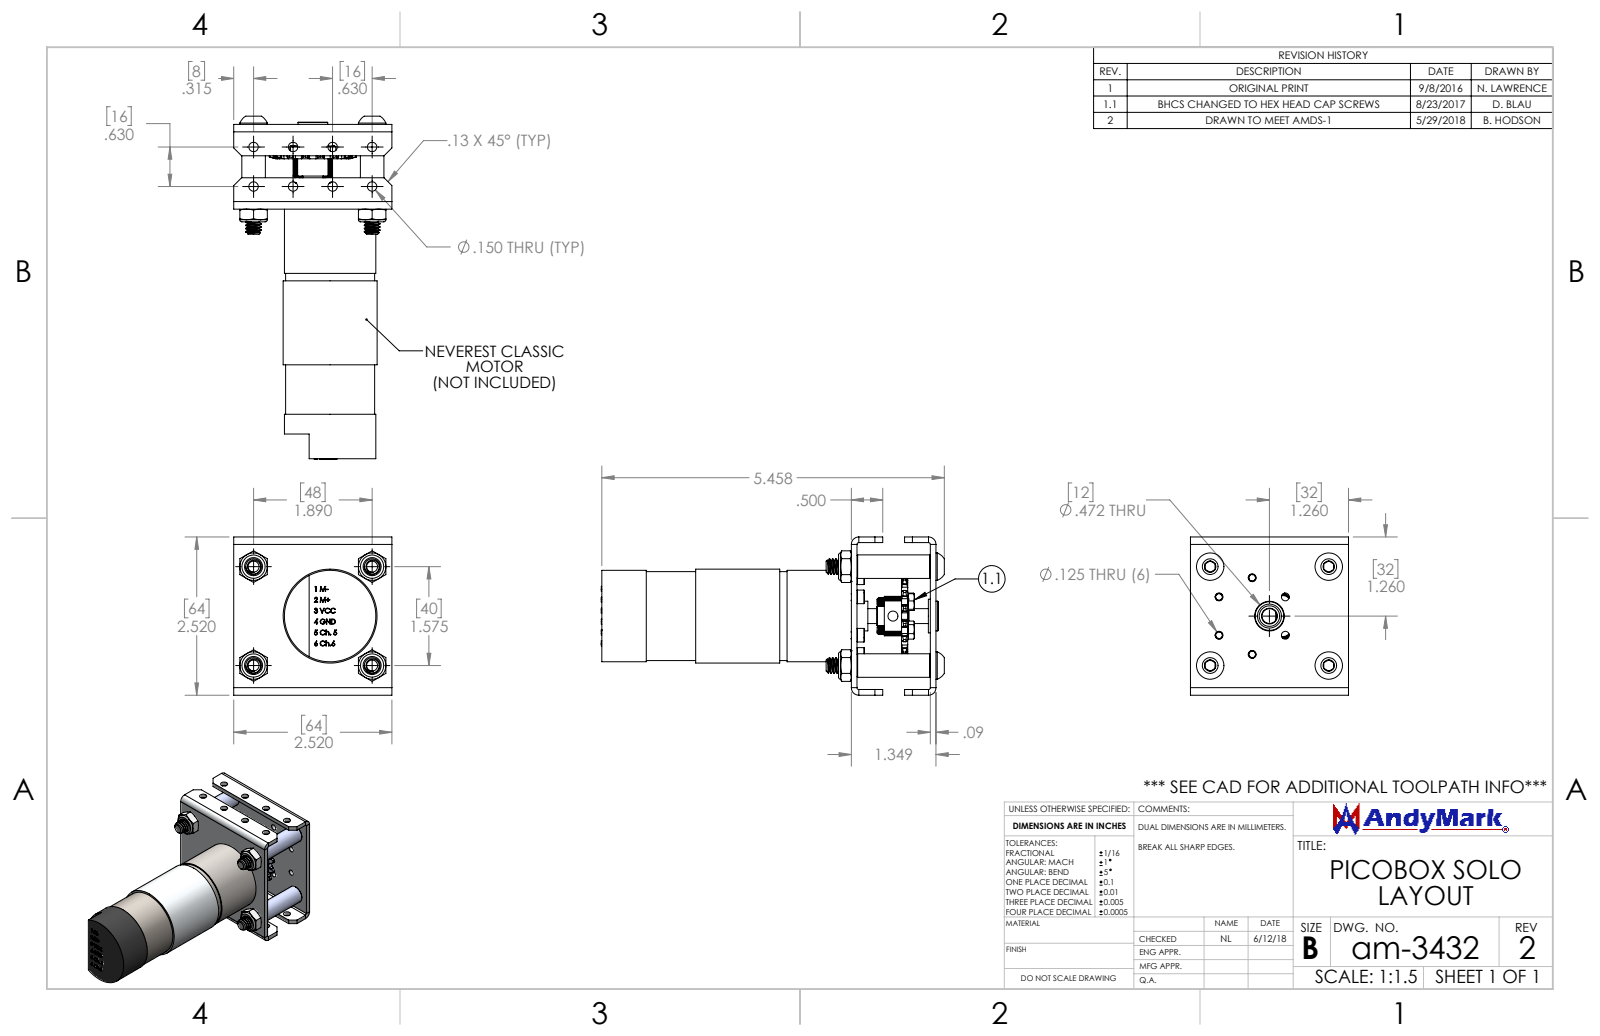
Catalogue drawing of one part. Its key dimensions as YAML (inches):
part_name: "am-3432 PicoBox Solo Assembly REV2; PicoBox Spacer; PicoBox Solo Plate Final; am-2964a NeveRest 40 (+7 more)"
step_written_by: "SolidWorks 2017 (AUTOMOTIVE_DESIGN)"
units: inches
bodies: {solids: 51, faces: 2234, planar: 502, cylindrical: 1114, other: 618}
overall_size: [5.466, 2.52, 2.52]
volume: 8.925
surface_area: 92.89
round_holes:
  - {diameter: 0.212, count: 12}
  - {diameter: 0.15, count: 8}
  - {diameter: 0.098, count: 6}
  - {diameter: 0.125, count: 4}
  - {diameter: 0.14, count: 4}
  - {diameter: 0.206, count: 4}
  - {diameter: 0.261, count: 4}
  - {diameter: 0.266, count: 4}
  - {diameter: 0.288, count: 4}
  - {diameter: 0.125, count: 2}
  - {diameter: 0.159, count: 1}
  - {diameter: 0.236, count: 1}
round_bosses_or_shafts:
  - {diameter: 0.217, count: 6}
  - {diameter: 0.118, count: 6}
  - {diameter: 0.093, count: 6}
  - {diameter: 0.437, count: 4}
  - {diameter: 0.375, count: 4}
  - {diameter: 0.25, count: 4}
  - {diameter: 0.138, count: 4}
  - {diameter: 1.496, count: 1}
partial_cylinders:
  - {radius: 0.01, count: 32}
  - {radius: 0.107, count: 32}
  - {radius: 0.171, count: 32}
  - {radius: 0.067, count: 16}
  - {radius: 0.029, count: 4}
  - {radius: 0.059, count: 4}
  - {radius: 0.106, count: 4}
  - {radius: 0.119, count: 4}
face_to_face_distances: [0.09, 0.09, 1.349, 1.259, 1.259, 1.169, 2.52, 2.43, 2.34, 2.43]
hole_center_spacings: [1.89, 0.63, 0.61, 0.891, 1.544, 2.441, 0.02, 0.315]
